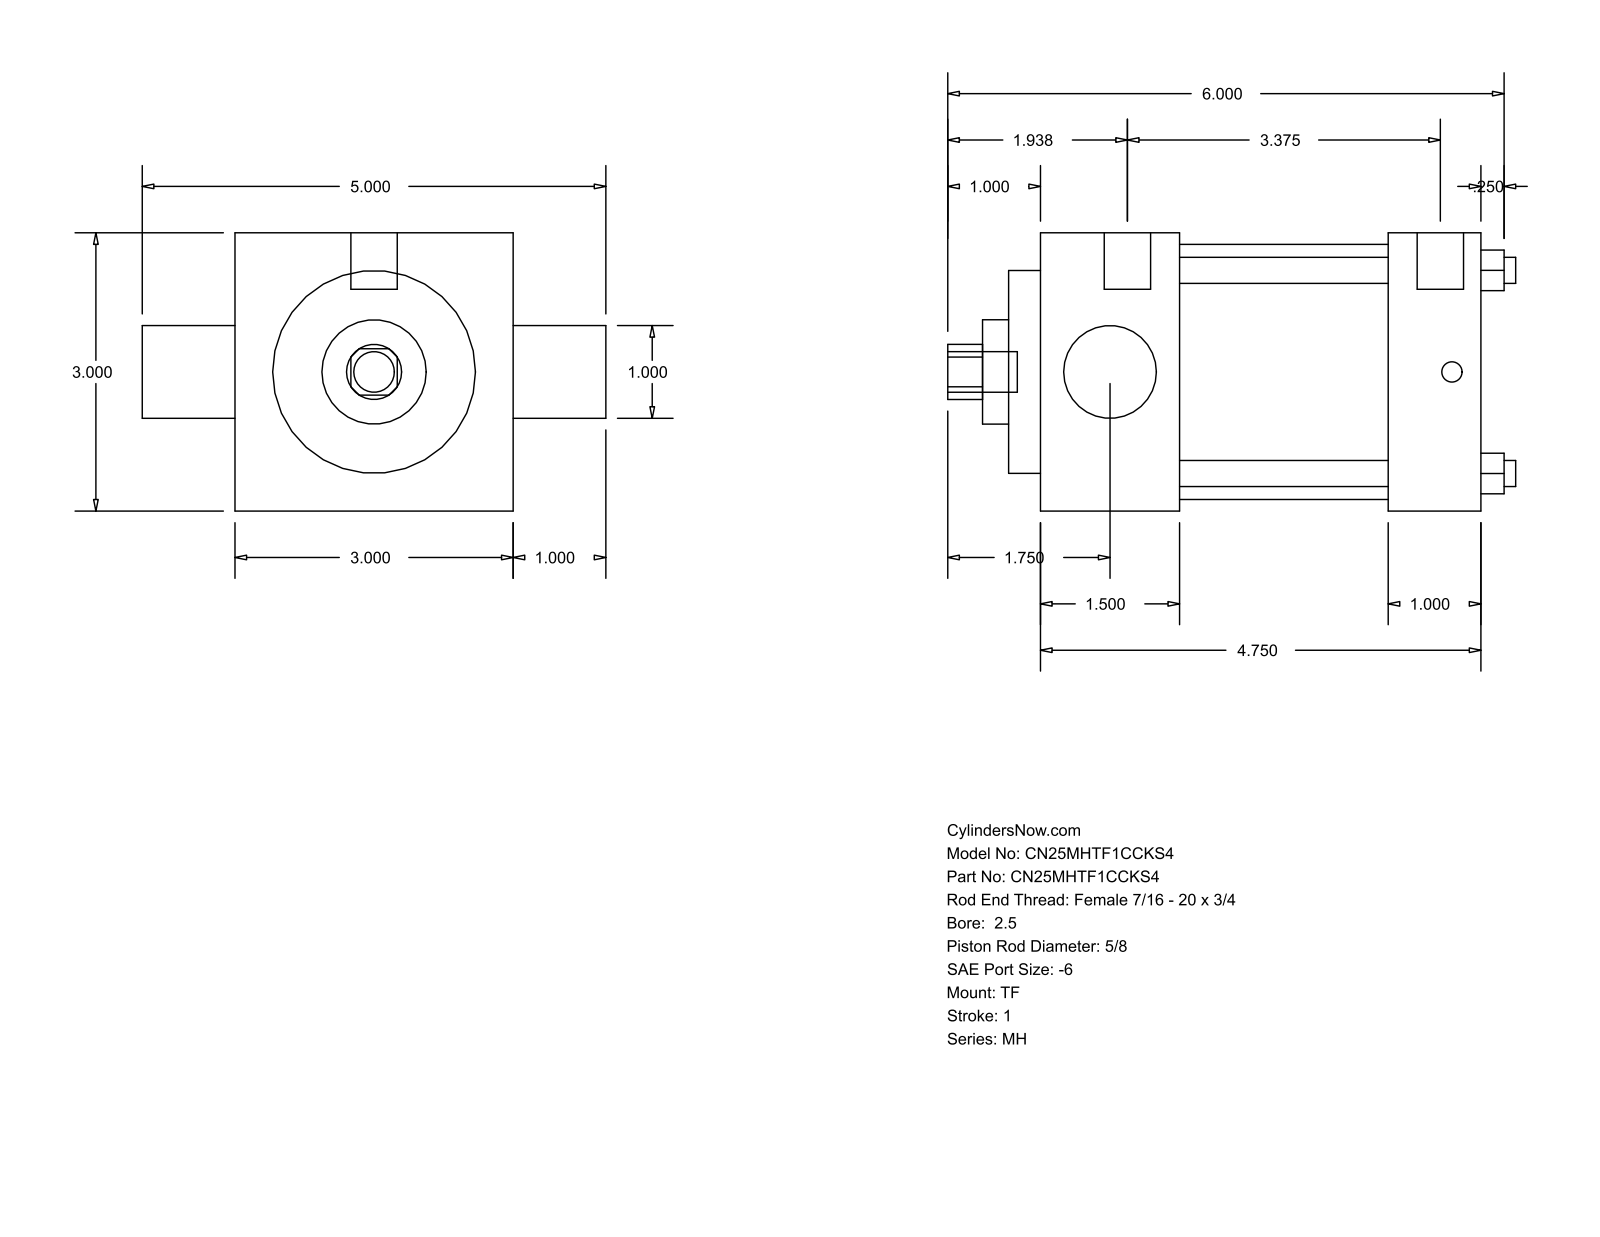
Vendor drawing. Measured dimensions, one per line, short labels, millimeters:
name: MH_TF__0250_0.625
written by: GSSL Pune (CONFIG_CONTROL_DESIGN)
unit: mm
bodies: 0 solids, 86 faces (61 planar, 25 cylindrical, 0 other)
size: 155.57 × 127 × 76.2
holes: 4× ⌀7.14, 1× ⌀15.88, 1× ⌀25.4, 1× ⌀28.57, 1× ⌀55.55, 1× ⌀69.85
bosses: 3× ⌀5.56, 2× ⌀12.7, 1× ⌀11.11
rounds: 1× R7.54
face distances: 76.2, 120.65, 25.4, 57.15, 38.1, 82.55, 95.25, 8.73, 46.83, 103.98
hole spacings: 39.33, 55.62, 78.66
